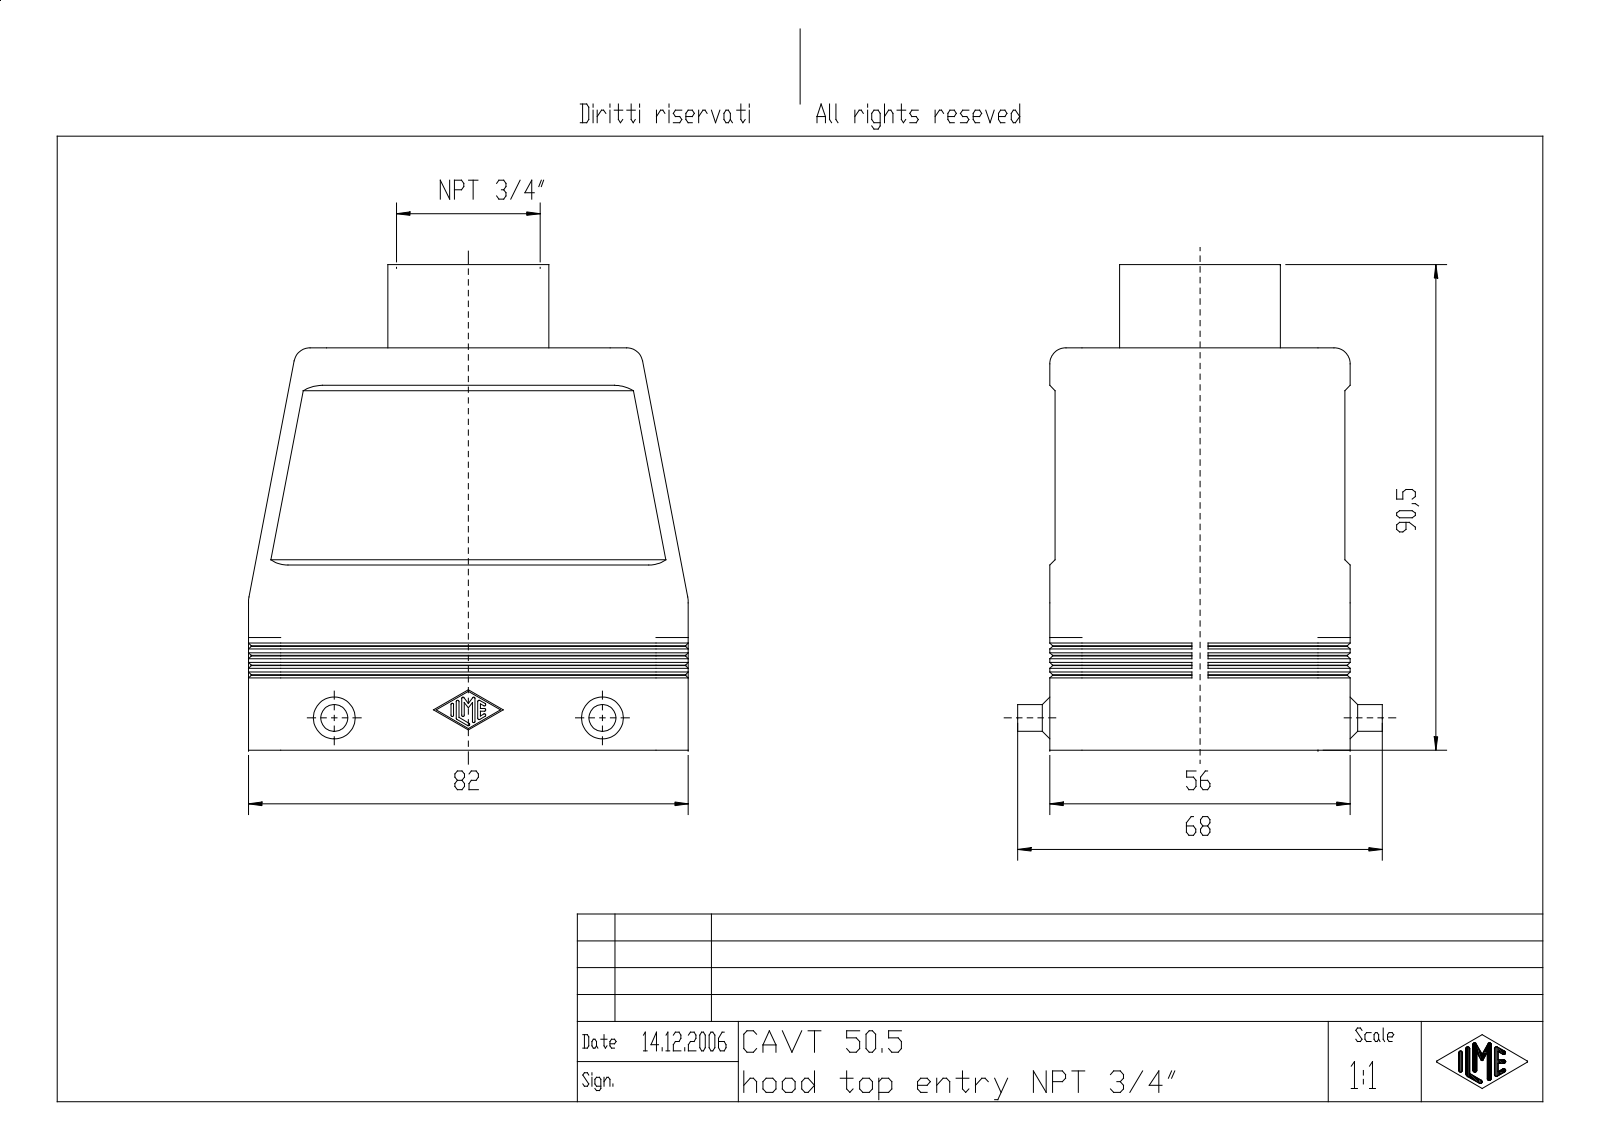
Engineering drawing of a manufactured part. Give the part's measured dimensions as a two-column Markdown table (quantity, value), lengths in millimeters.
| quantity | value |
| --- | --- |
| part name | MSBO7607 |
| STEP written by | Creo Elements/Direct Modeling 18.0B 02-Dec-2011 (C) Parametric Technology GmbH (AUTOMOTIVE_DESIGN) |
| units | millimeters |
| bodies | 1 solid, 371 faces (203 planar, 118 cylindrical, 50 other) |
| overall size | 90.5 × 82 × 68 |
| volume | 86 242 mm³ |
| surface area | 49 633 mm² |
| round holes (diameter × count) | 3.5 × 8, 2.46 × 6, 2.46 × 2 |
| round bosses / shafts (diameter × count) | 5 × 2, 40 × 1, 30 × 1 |
| partial cylindrical surfaces (radius × count) | 0.25 × 14, 6 × 10, 2 × 8, 3 × 8, 5.5 × 4 |
| main face-to-face distances | 3, 53, 50, 2, 55, 1, 52, 56, 54, 11.25 |
| hole center spacings | 16, 24, 66, 67.91, 70.23, 8, 40, 66.48 |
